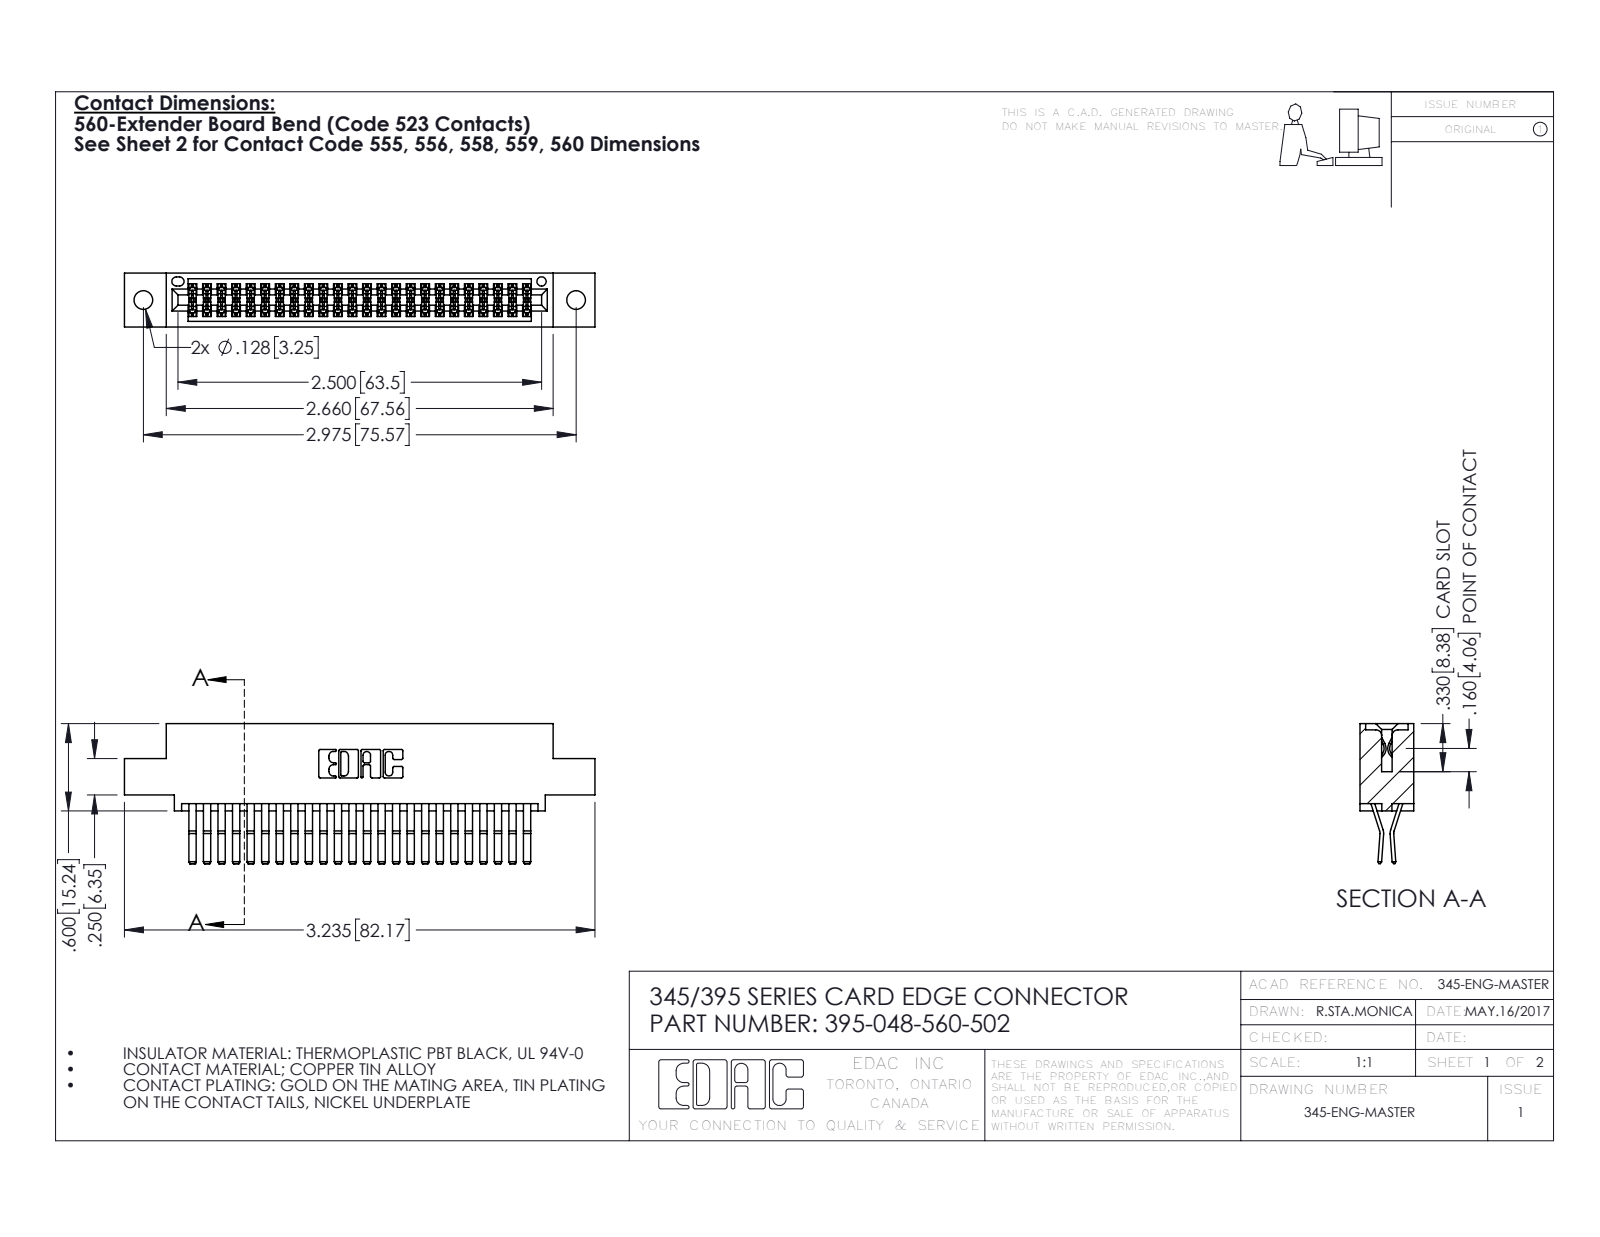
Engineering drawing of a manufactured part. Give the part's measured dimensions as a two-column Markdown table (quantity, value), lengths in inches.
| quantity | value |
| --- | --- |
| part name | 345-292-001_560 Tail; 345 Part_0.110 Offset - 0.128 Dia; 395-048-560-502 |
| STEP written by | SolidWorks 2016 (CONFIG_CONTROL_DESIGN) |
| units | inches |
| bodies | 49 solids, 2626 faces (1668 planar, 958 cylindrical, 0 other) |
| overall size | 3.235 × 0.962 × 0.37 |
| volume | 0.489 in³ |
| surface area | 18.81 in² |
| round holes (diameter × count) | 0.128 × 2, 0.064 × 1 |
| partial cylindrical surfaces (radius × count) | 0.006 × 72, 0.01 × 22, 0.007 × 6, 0.031 × 6, 0.026 × 3, 0.01 × 2, 0.014 × 2, 0.019 × 2 |
| main face-to-face distances | 0.025, 0.298, 0.072, 0.37, 0.2, 0.098, 0.272, 0.225, 0.175, 0.149 |
| hole center spacings | 0.27, 2.741, 2.975 |
